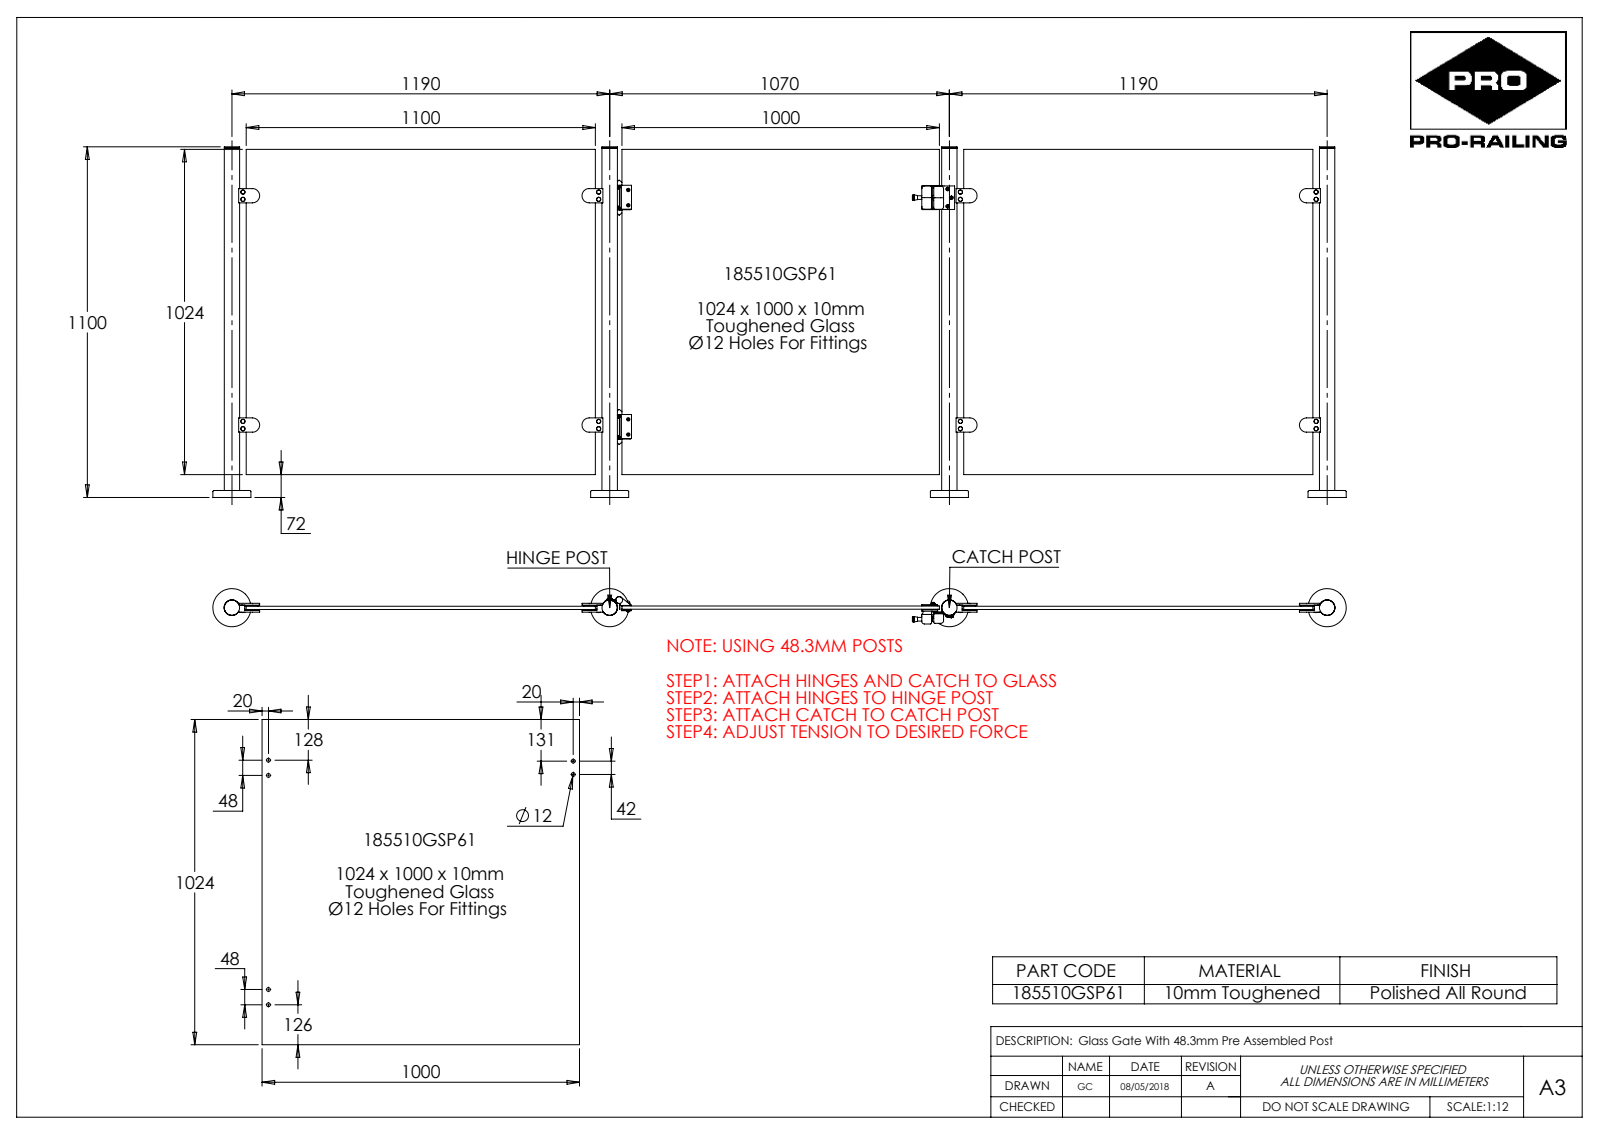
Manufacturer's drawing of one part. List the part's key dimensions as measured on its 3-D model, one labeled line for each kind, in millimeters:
Part name (STEP PRODUCT): 185510GSP61
STEP written by: SolidWorks 2020 (CONFIG_CONTROL_DESIGN)
Units: millimetres
Bodies: 1 solid, 18 faces (6 planar, 12 cylindrical, 0 other)
Overall size (bounding box): 1024 × 1000 × 10
Volume: 10 230 000 mm³ · Surface area: 2 089 000 mm²
Round holes (diameter × count): ⌀12 ×6
Main face-to-face distances: 10, 1000, 1024
Hole centre spacings: 48, 722, 960, 961.05, 42, 674, 770, 1174.7
